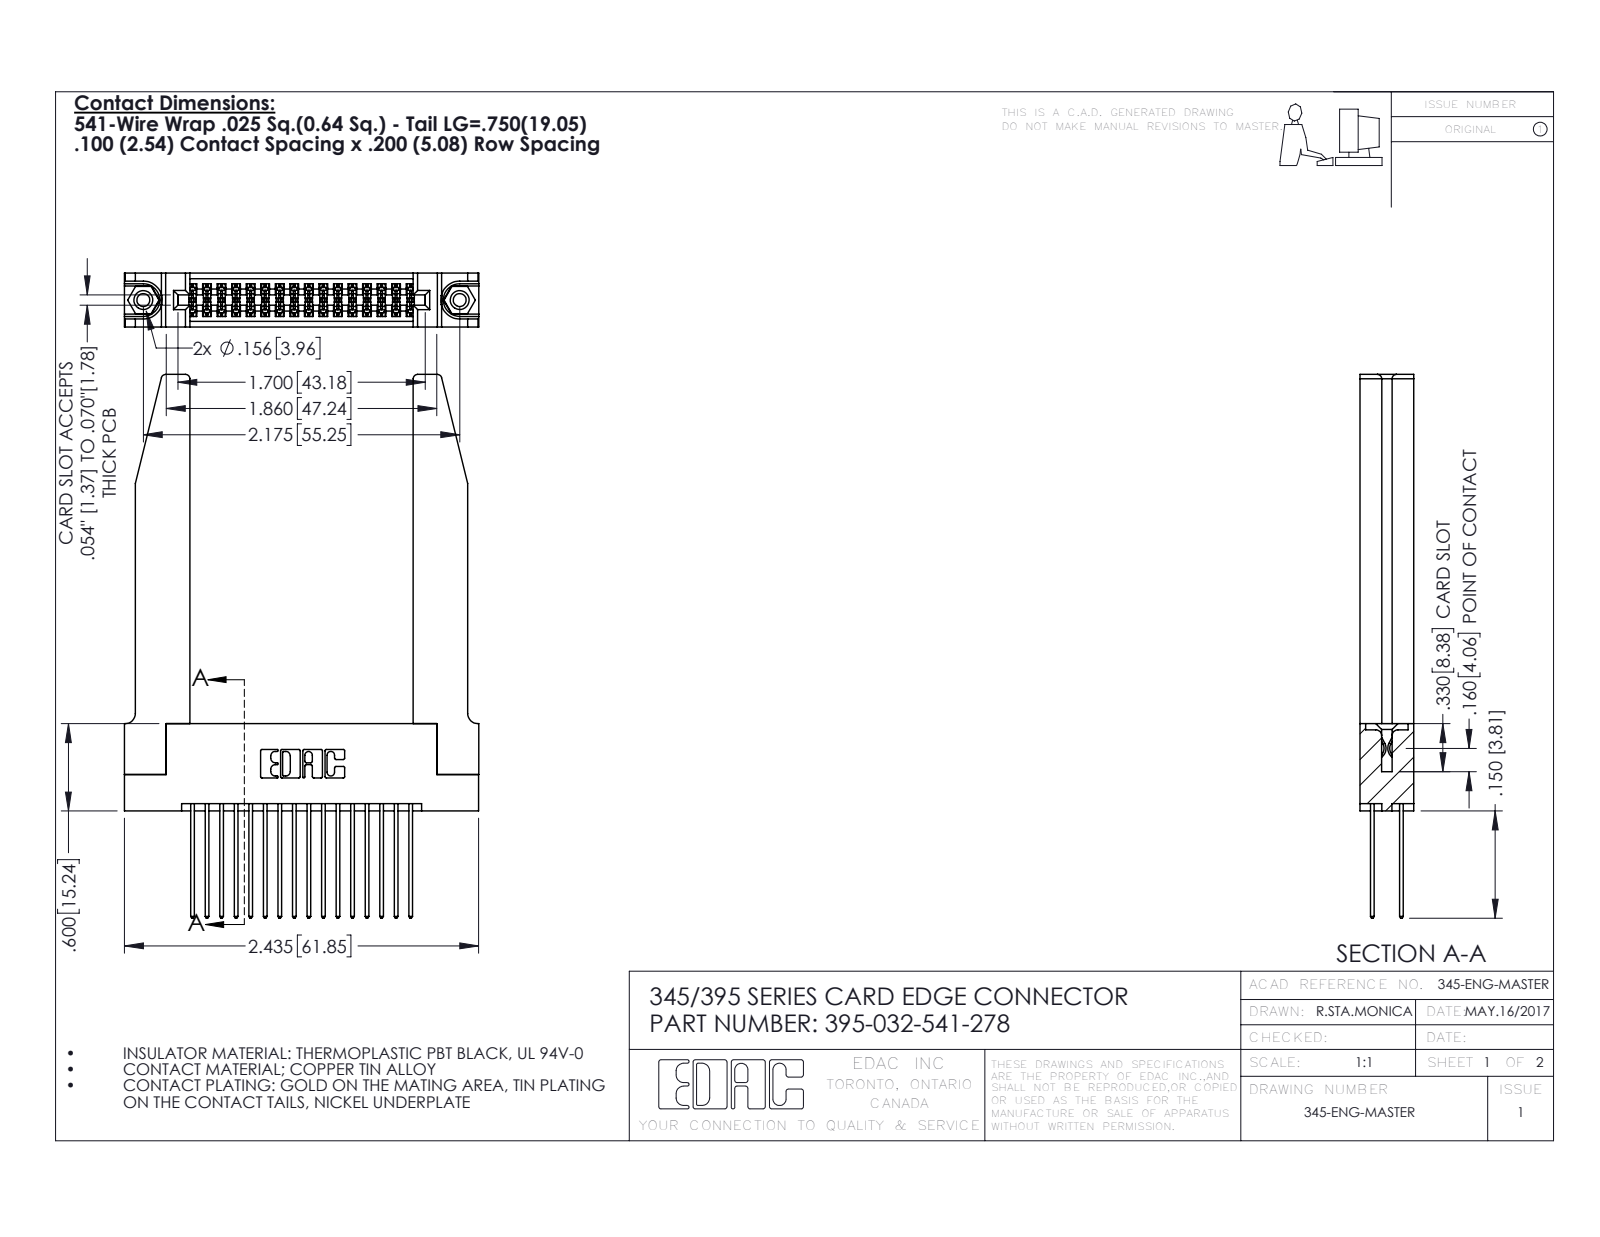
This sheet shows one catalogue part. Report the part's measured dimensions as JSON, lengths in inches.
{"part_name": "345-220-078_345-220-078; 345 Part_Flush Mounting Lugs - 0.156 Dia-TH; 395-032-541-278; 345-292-001_345-293-141 (+1 more)", "step_written_by": "SolidWorks 2016 (CONFIG_CONTROL_DESIGN)", "units": "inches", "bodies": {"solids": 37, "faces": 1960, "planar": 1278, "cylindrical": 630, "other": 52}, "overall_size": [3.737, 2.436, 0.37], "volume_in3": 0.837, "surface_area_in2": 24.8, "round_holes": [[0.089, 2], [0.125, 2], [0.156, 2], [0.064, 1]], "round_bosses_or_shafts": [[0.155, 2]], "partial_cylinders_radius": [[0.006, 48], [0.01, 32], [0.01, 22], [0.03, 8], [0.007, 6], [0.031, 6], [0.026, 3], [0.014, 2]], "face_to_face_distances": [0.37, 0.072, 0.298, 0.2, 0.098, 0.272, 0.025, 0.225, 0.148, 0.15], "hole_center_spacings": [0.27, 1.942, 2.175]}
